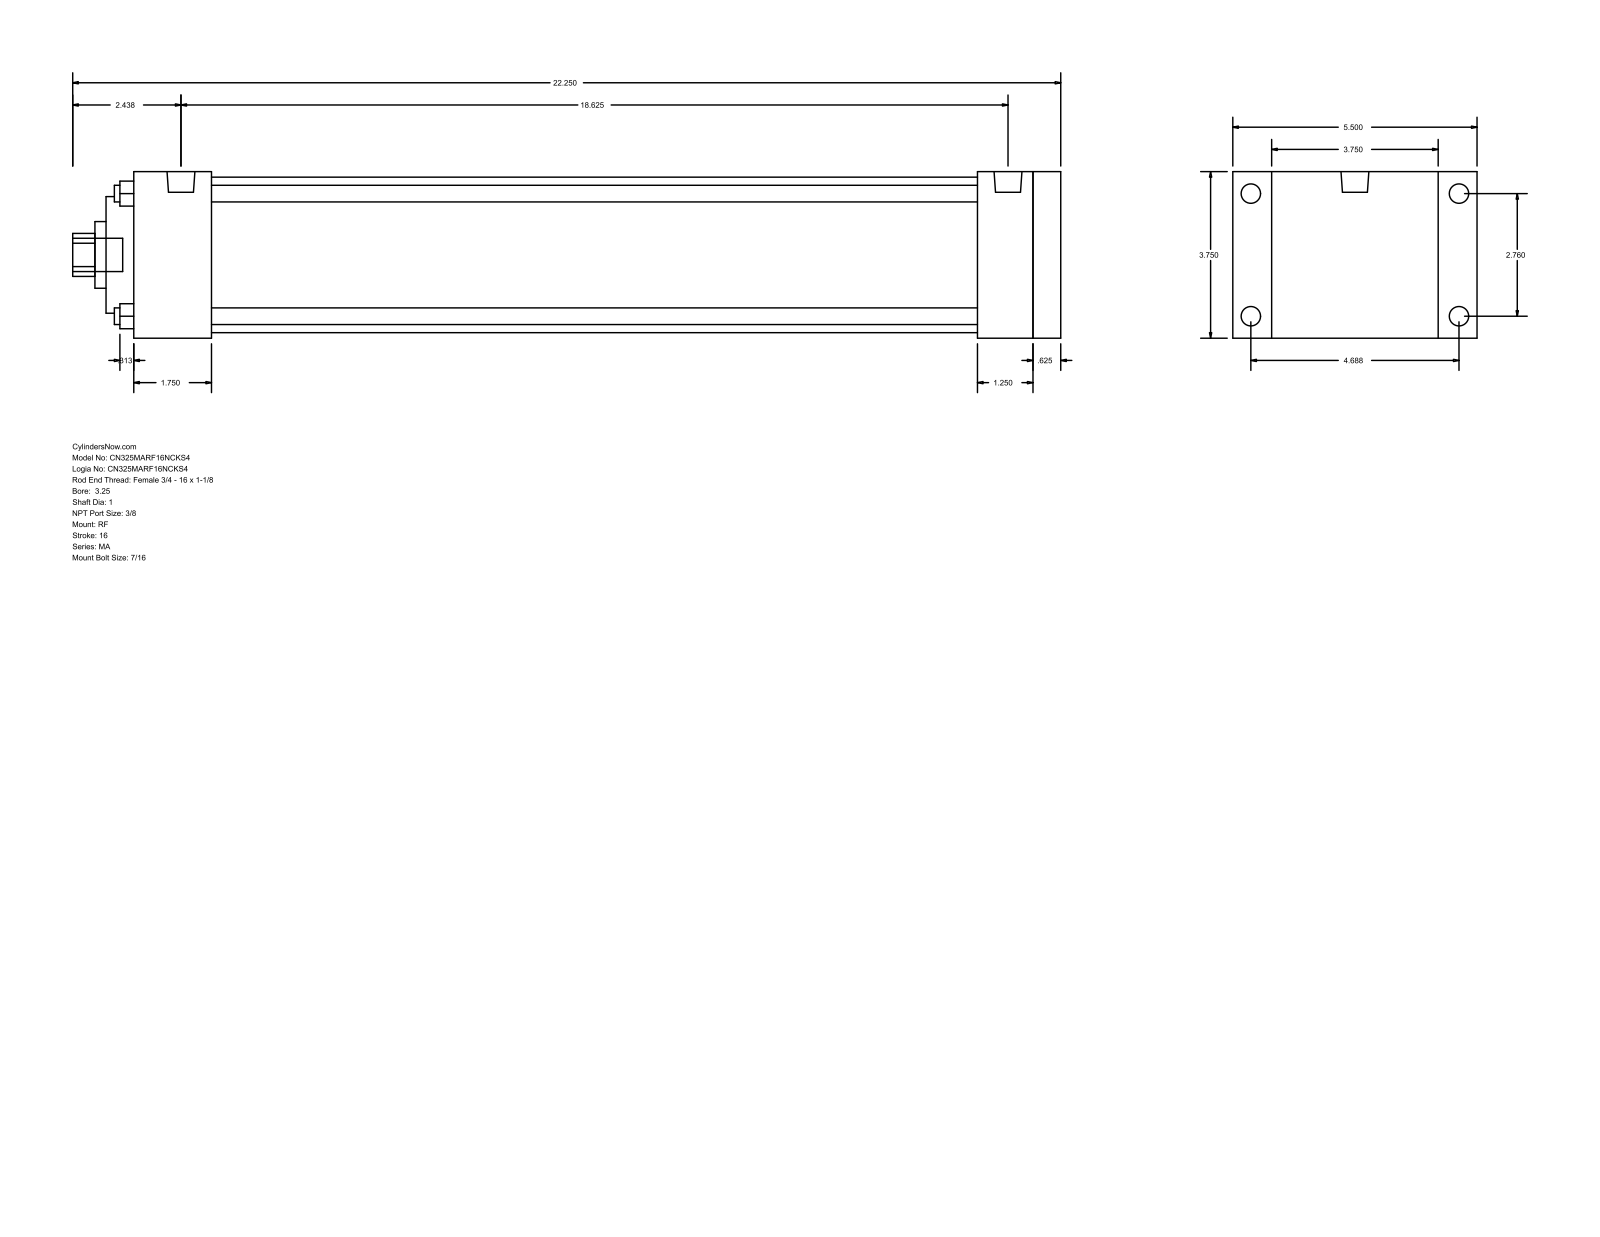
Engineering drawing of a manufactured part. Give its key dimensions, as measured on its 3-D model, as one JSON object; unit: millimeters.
{"part_name": "MA_RF__0325_1", "step_written_by": "GSSL Pune (CONFIG_CONTROL_DESIGN)", "units": "millimeters", "bodies": {"solids": 0, "faces": 94, "planar": 65, "cylindrical": 29, "other": 0}, "overall_size": [565.15, 139.7, 95.25], "round_holes": [[9.53, 4], [25.4, 1], [38.1, 1], [66.67, 1], [88.9, 1]], "round_bosses_or_shafts": [[11.11, 8], [15.93, 2], [19.05, 1]], "partial_cylinders_radius": [[12.29, 1]], "face_to_face_distances": [95.24, 530.23, 514.35, 15.88, 22.23, 117.47, 15.87, 482.6, 31.75, 47.63], "hole_center_spacings": [49.57, 70.1, 99.14]}
